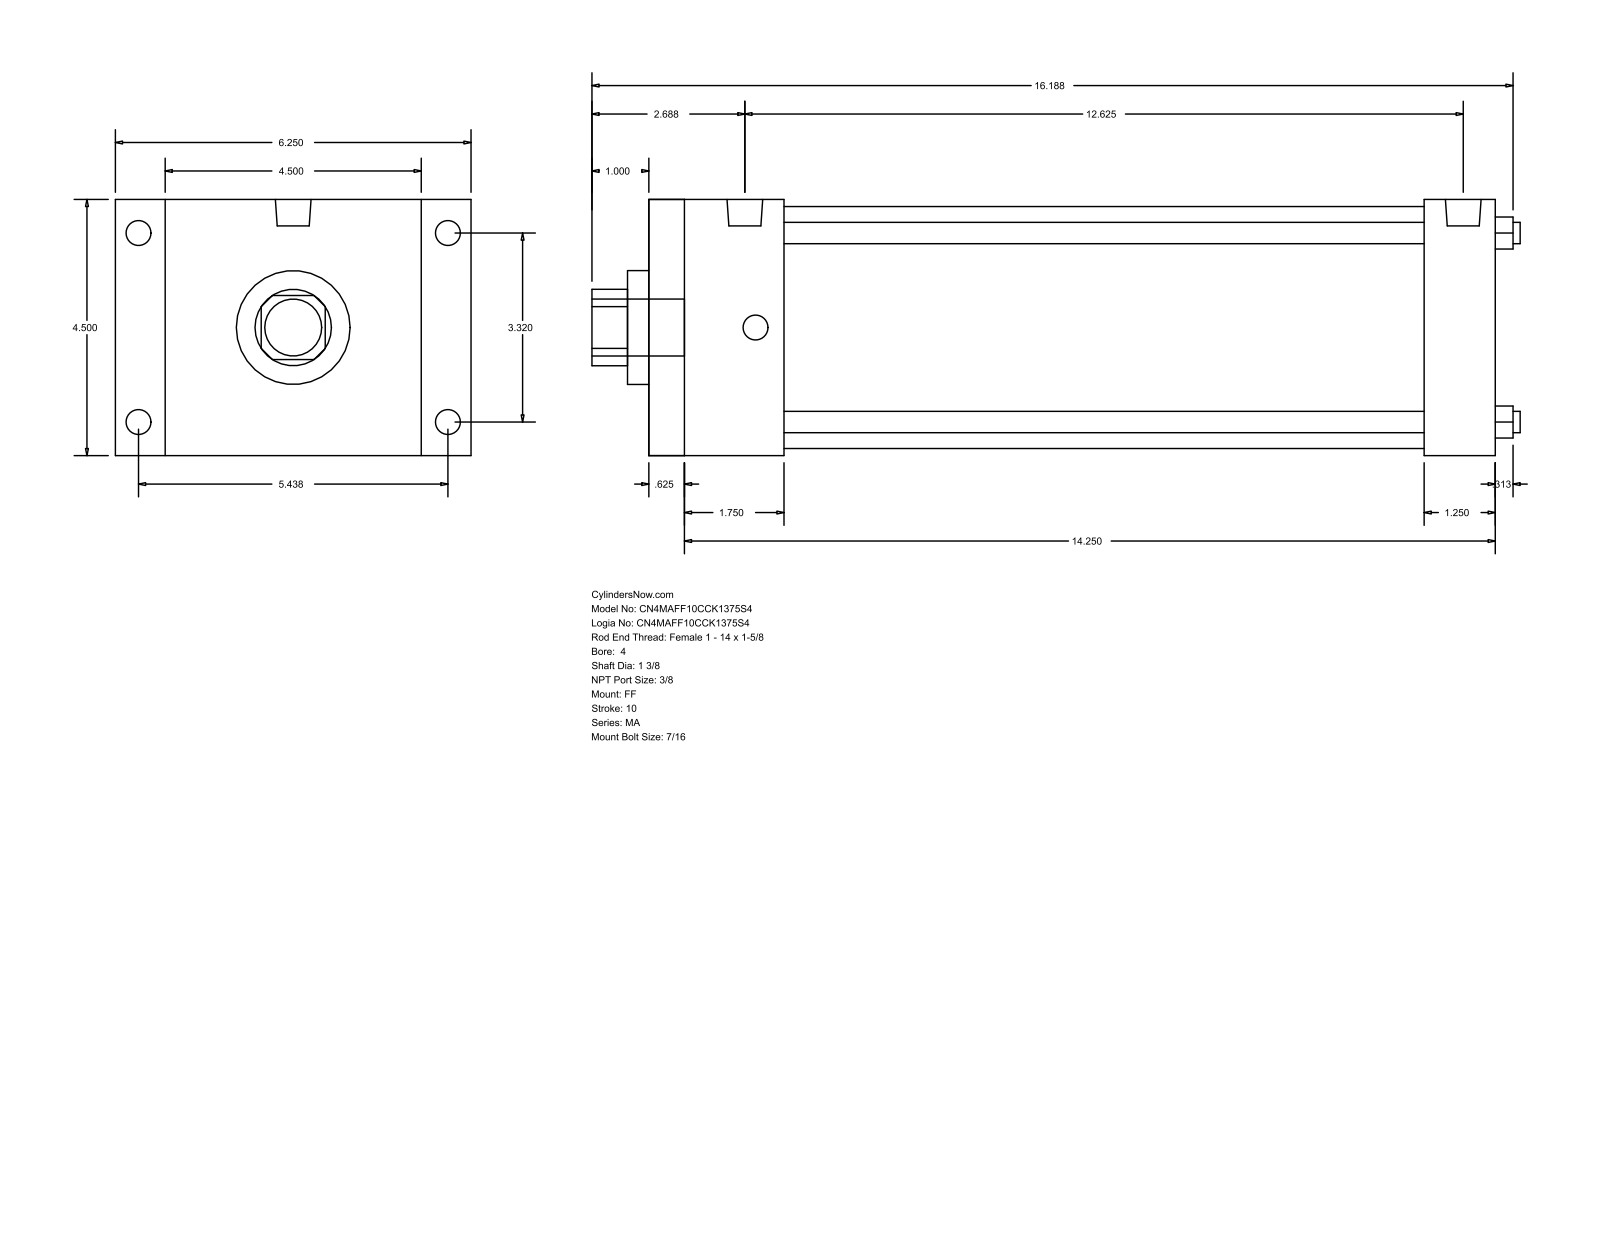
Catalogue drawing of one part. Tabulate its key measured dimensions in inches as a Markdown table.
| quantity | value |
| --- | --- |
| part name | MA_FF__0400_1.375 |
| STEP written by | GSSL Pune (CONFIG_CONTROL_DESIGN) |
| units | inches |
| bodies | 0 solids, 92 faces (64 planar, 28 cylindrical, 0 other) |
| overall size | 16.313 × 6.25 × 4.5 |
| round holes (diameter × count) | 0.375 × 4, 1.375 × 1, 2 × 1, 4.25 × 1 |
| round bosses / shafts (diameter × count) | 0.437 × 8, 0.627 × 2, 1 × 1 |
| partial cylindrical surfaces (radius × count) | 0.672 × 1 |
| main face-to-face distances | 4.5, 14.875, 0.625, 14.25, 0.875, 5.375, 13.625, 13, 1.25, 2.375 |
| hole center spacings | 2.347, 3.32, 4.695 |
